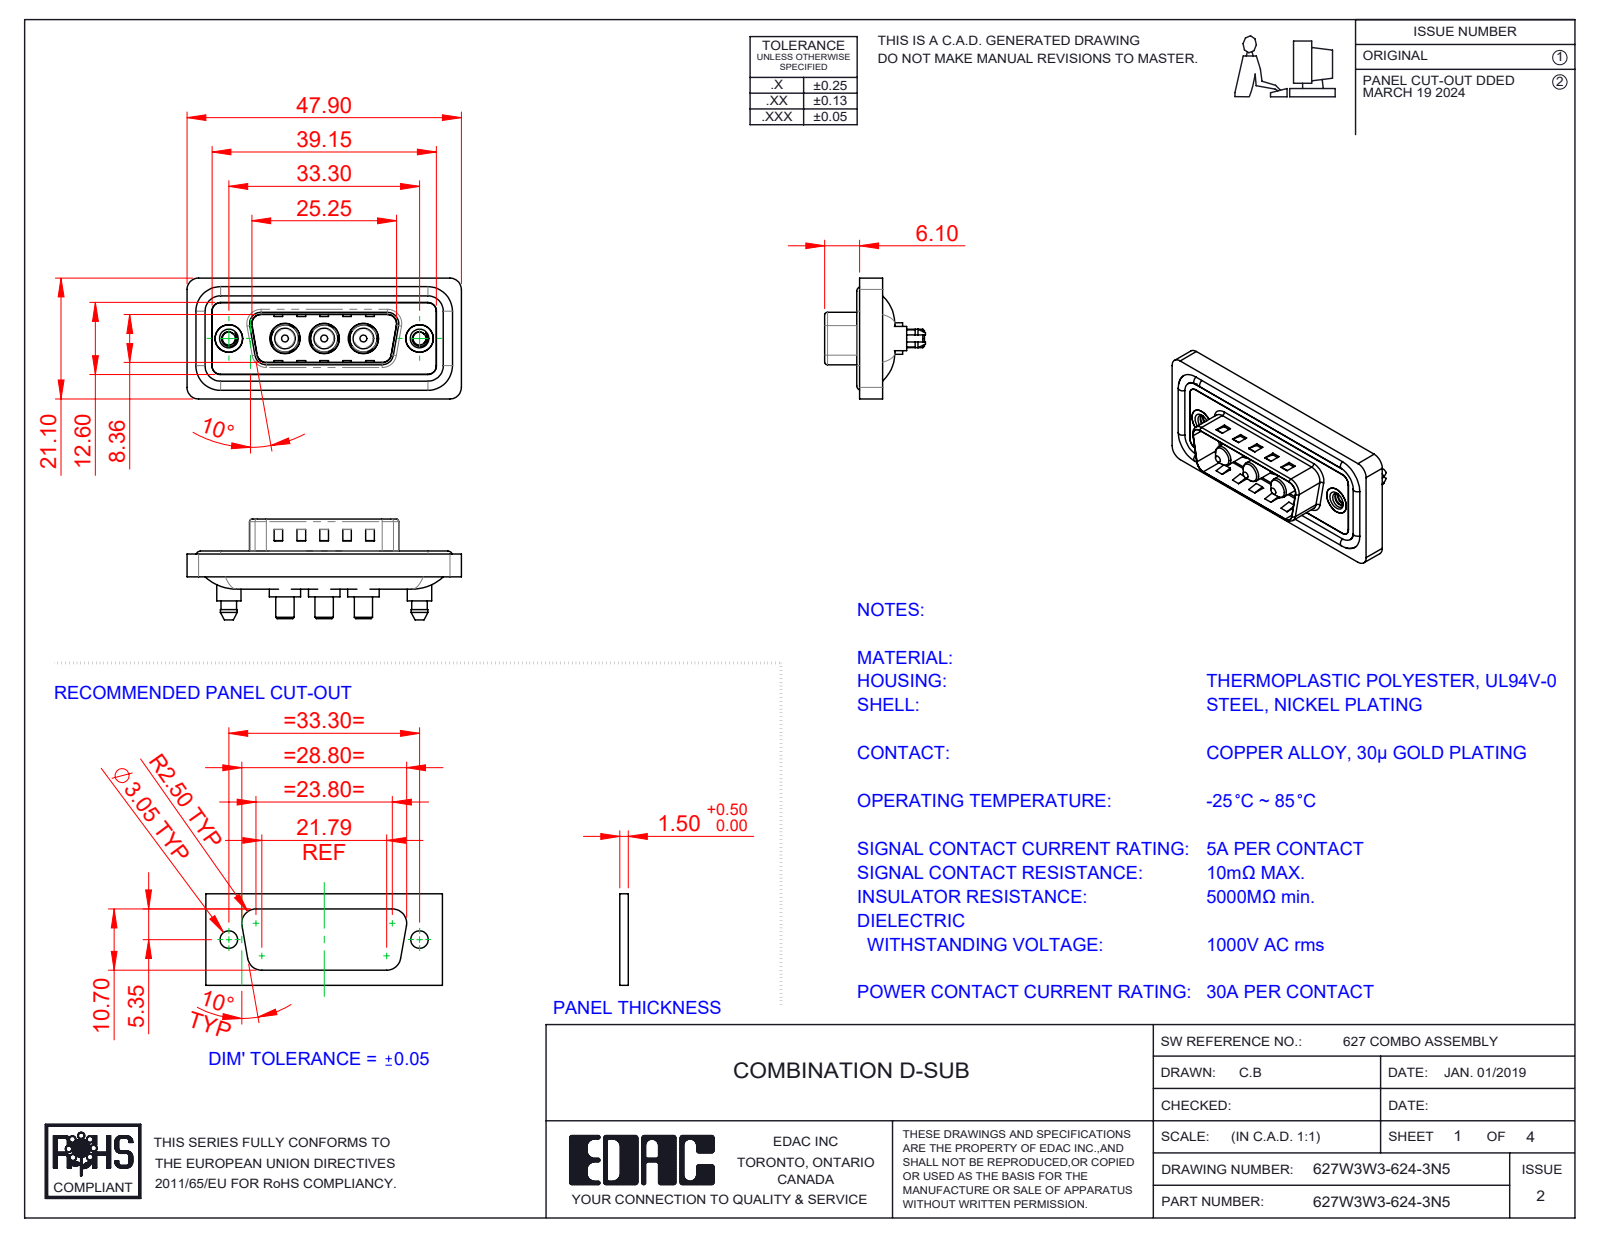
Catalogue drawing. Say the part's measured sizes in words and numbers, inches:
The part is named "627Combo Housing_3W3; Power Pin_30A S; 627Combo Shell Front_15 Contacts; 627W3W3-624-3N5 (+3 more)". Its 3-D file was written by "SolidWorks 2023 (CONFIG_CONTROL_DESIGN)". It is 13 solids with 614 faces: 223 planar, 273 cylindrical and 118 other. Overall it measures 1.886 by 0.831 by 0.693 inches. Its volume is 0.35 cubic inches and its surface area 14.11 square inches. Round holes: 3 of diameter 0.191, 3 of diameter 0.209, 2 of diameter 0.089, 2 of diameter 0.157, 2 of diameter 0.189, 2 of diameter 0.197. Round bosses or shafts: 4 of diameter 0.063, 3 of diameter 0.217, 3 of diameter 0.205, 3 of diameter 0.187, 3 of diameter 0.148, 3 of diameter 0.142, 3 of diameter 0.126, 2 of diameter 0.213. Partial cylindrical surfaces (rounded edges, fillets, slot ends): 28 of radius 0.059, 20 of radius 0.079, 10 of radius 0.063, 8 of radius 0.02, 4 of radius 0.01, 4 of radius 0.024, 4 of radius 0.026, 4 of radius 0.035. The main face-to-face distances are 0.016, 0.043, 0.059, 0.122, 0.063, 0.02, 0.114, 0.157, 0.028, 0.032. The hole center spacings are 0.27, 0.386, 0.656, 0.925, 0.539, 1.311.
